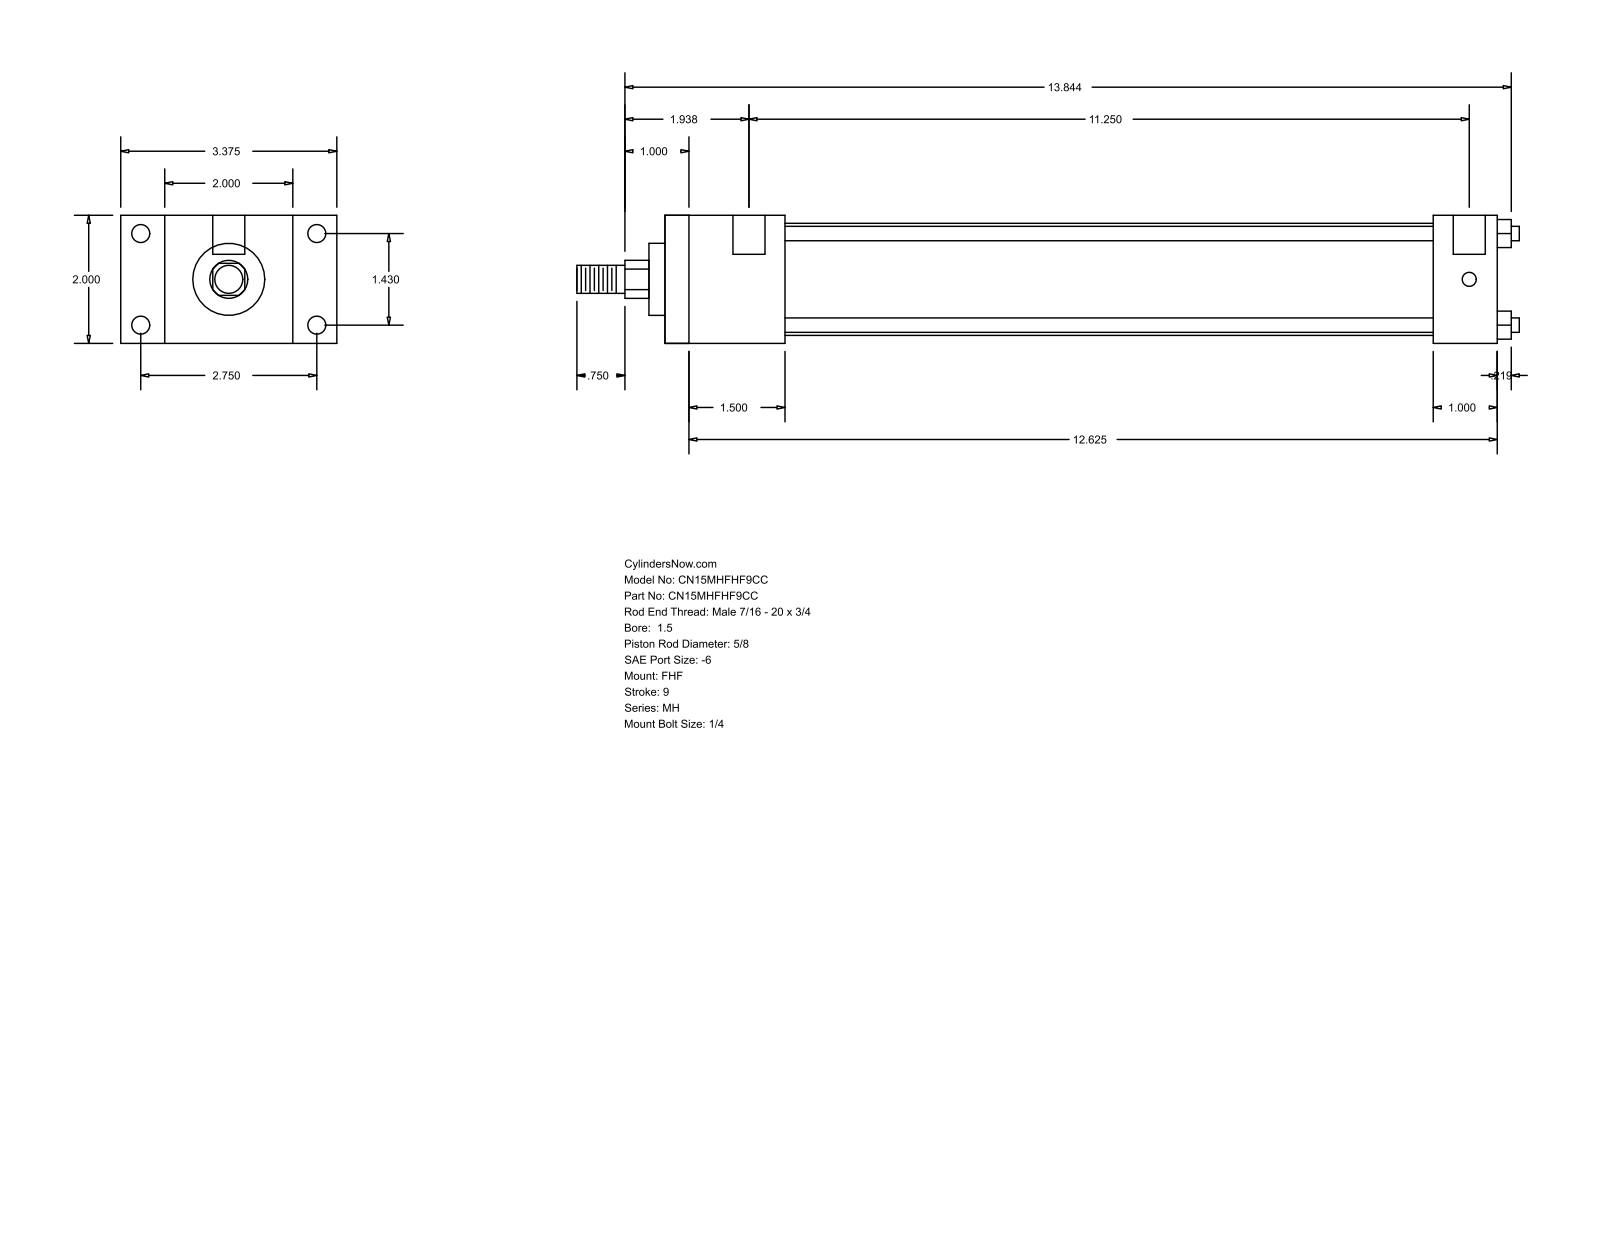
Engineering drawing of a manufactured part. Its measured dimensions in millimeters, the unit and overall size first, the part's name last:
Units: millimetres
Overall size (bounding box): 373.86 × 85.72 × 50.8
Round holes (diameter × count): ⌀5.56 ×4, ⌀7.14 ×4, ⌀12.7 ×2
Round bosses / shafts (diameter × count): ⌀5.71 ×4, ⌀44.45 ×1, ⌀28.57 ×1, ⌀15.88 ×1, ⌀11.11 ×1
Partial cylindrical surfaces — rounded edges, fillets, slot ends (radius × count): R7.54 ×1
Main face-to-face distances: 50.8, 17.46, 68.26, 47.62, 85.72, 330.19, 282.57, 304.8, 257.18, 25.39
Hole centre spacings: 36.32, 69.84, 78.72, 288.92, 3.17, 285.75
Bodies: 0 solids, 88 faces (60 planar, 28 cylindrical, 0 other)
Part name (STEP PRODUCT): MH_FHF__0150_0.625
STEP written by: GSSL Pune (CONFIG_CONTROL_DESIGN)
